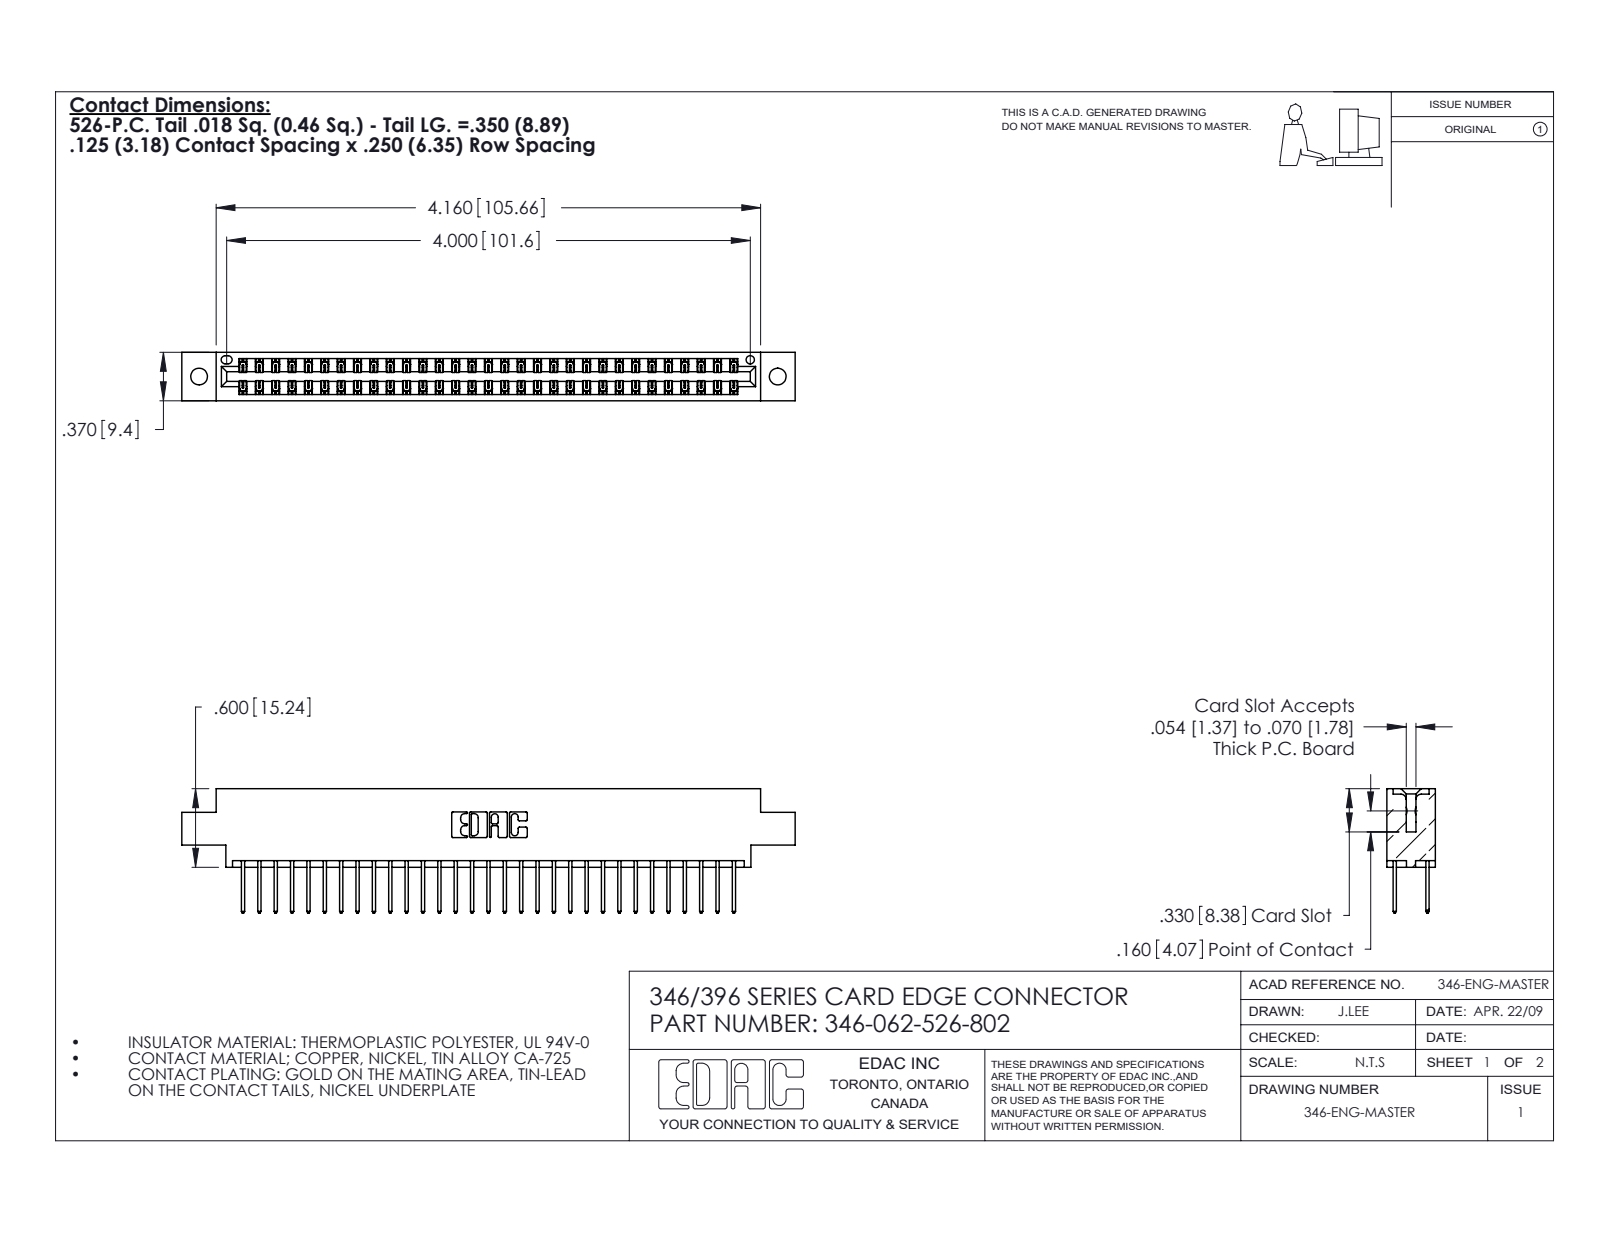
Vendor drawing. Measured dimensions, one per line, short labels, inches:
name: 346-062-526-802; 345-292-001_345-293-126; 346 Part_0.170 Offset - 0.128 Dia
written by: SolidWorks 2020 (CONFIG_CONTROL_DESIGN)
unit: in
bodies: 63 solids, 3350 faces (2250 planar, 1100 cylindrical, 0 other)
size: 4.685 × 0.95 × 0.37
volume: 0.697 in³; area: 24.65 in²
holes: 2× ⌀0.128, 1× ⌀0.064
rounds: 93× R0.006, 62× R0.01, 22× R0.01, 6× R0.007, 6× R0.031, 3× R0.026, 2× R0.014, 2× R0.022
face distances: 0.048, 0.322, 0.25, 0.37, 0.072, 0.298, 0.025, 0.275, 0.148, 0.222
hole spacings: 0.246, 4.212, 4.42
